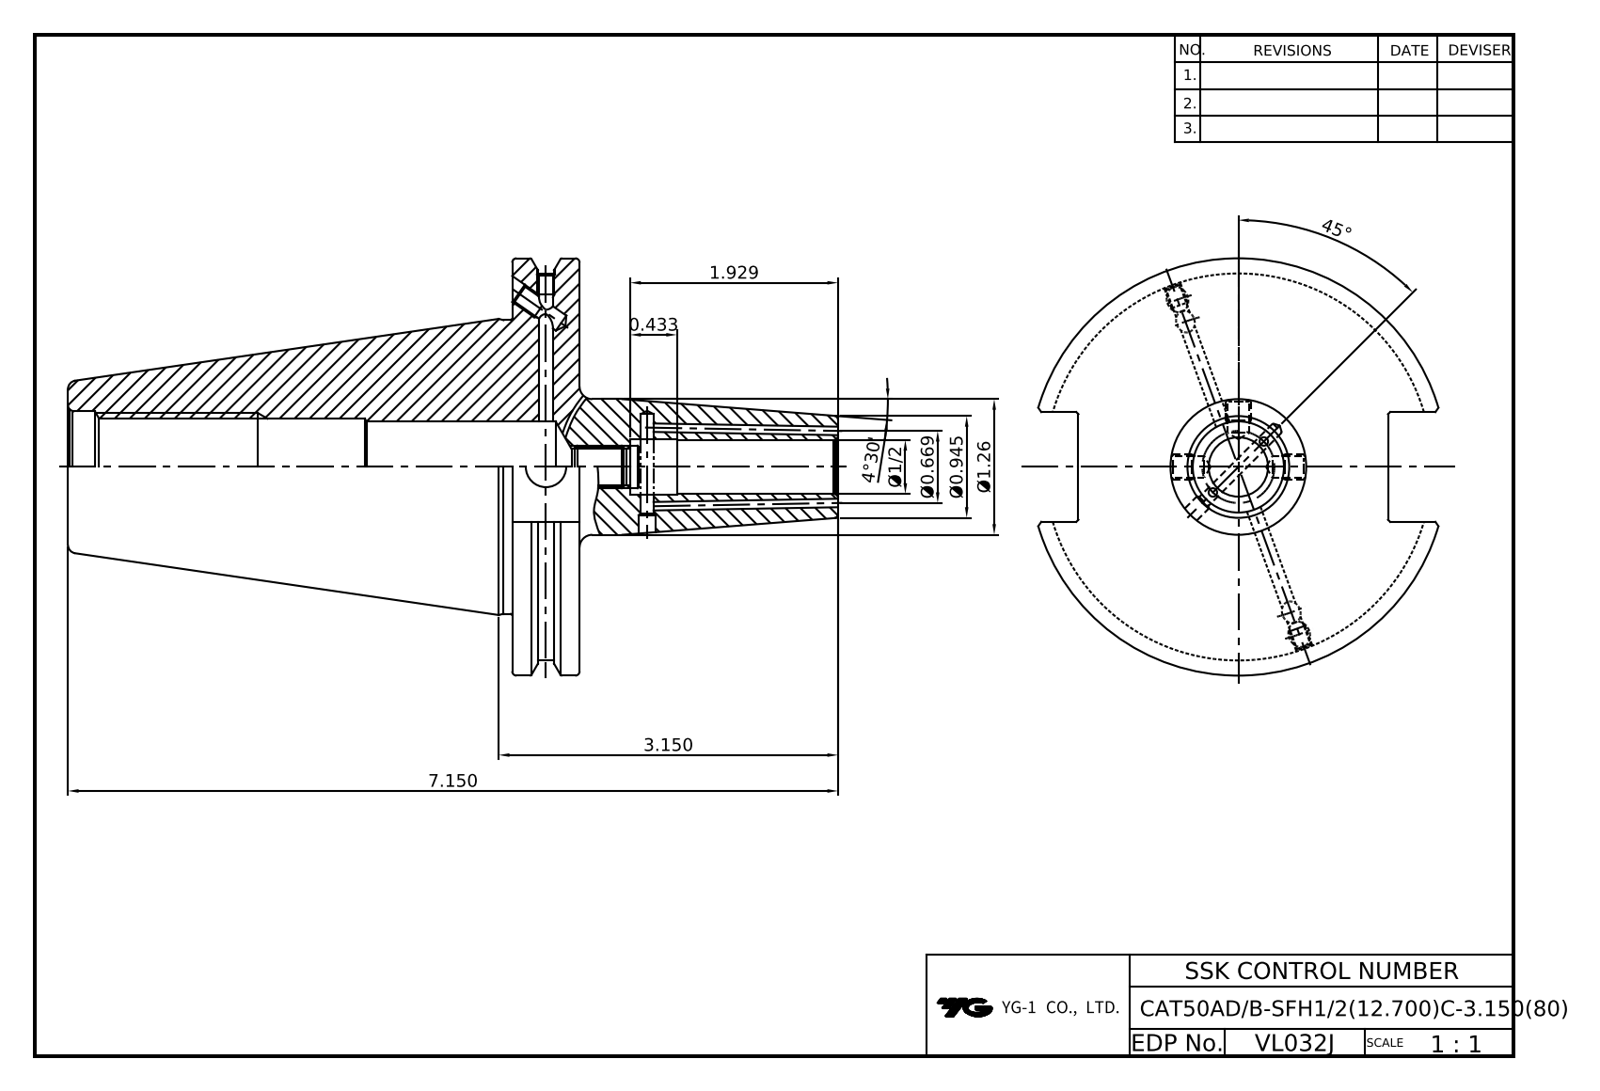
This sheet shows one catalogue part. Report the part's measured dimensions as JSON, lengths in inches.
{"part_name": "LO-CAT50ADB-SFH12.7C-80", "step_written_by": "Autodesk Inventor 2024 (AUTOMOTIVE_DESIGN)", "units": "inches", "bodies": {"solids": 1, "faces": 90, "planar": 39, "cylindrical": 29, "other": 22}, "overall_size": [7.15, 3.875, 3.728], "volume_in3": 21.51, "surface_area_in2": 82.16, "round_holes": [[0.098, 2], [0.128, 2], [0.163, 2], [0.165, 2], [0.197, 2], [0.351, 1], [0.375, 1], [0.5, 1], [0.547, 1], [0.846, 1], [0.865, 1], [1.031, 1]], "round_bosses_or_shafts": [[3.875, 1], [3.594, 1], [2.726, 1], [1.26, 1]], "face_to_face_distances": [0.625, 4.125, 4.75, 2.875, 1.02, 7.15, 3.025, 2.4, 4.363, 0.238]}
